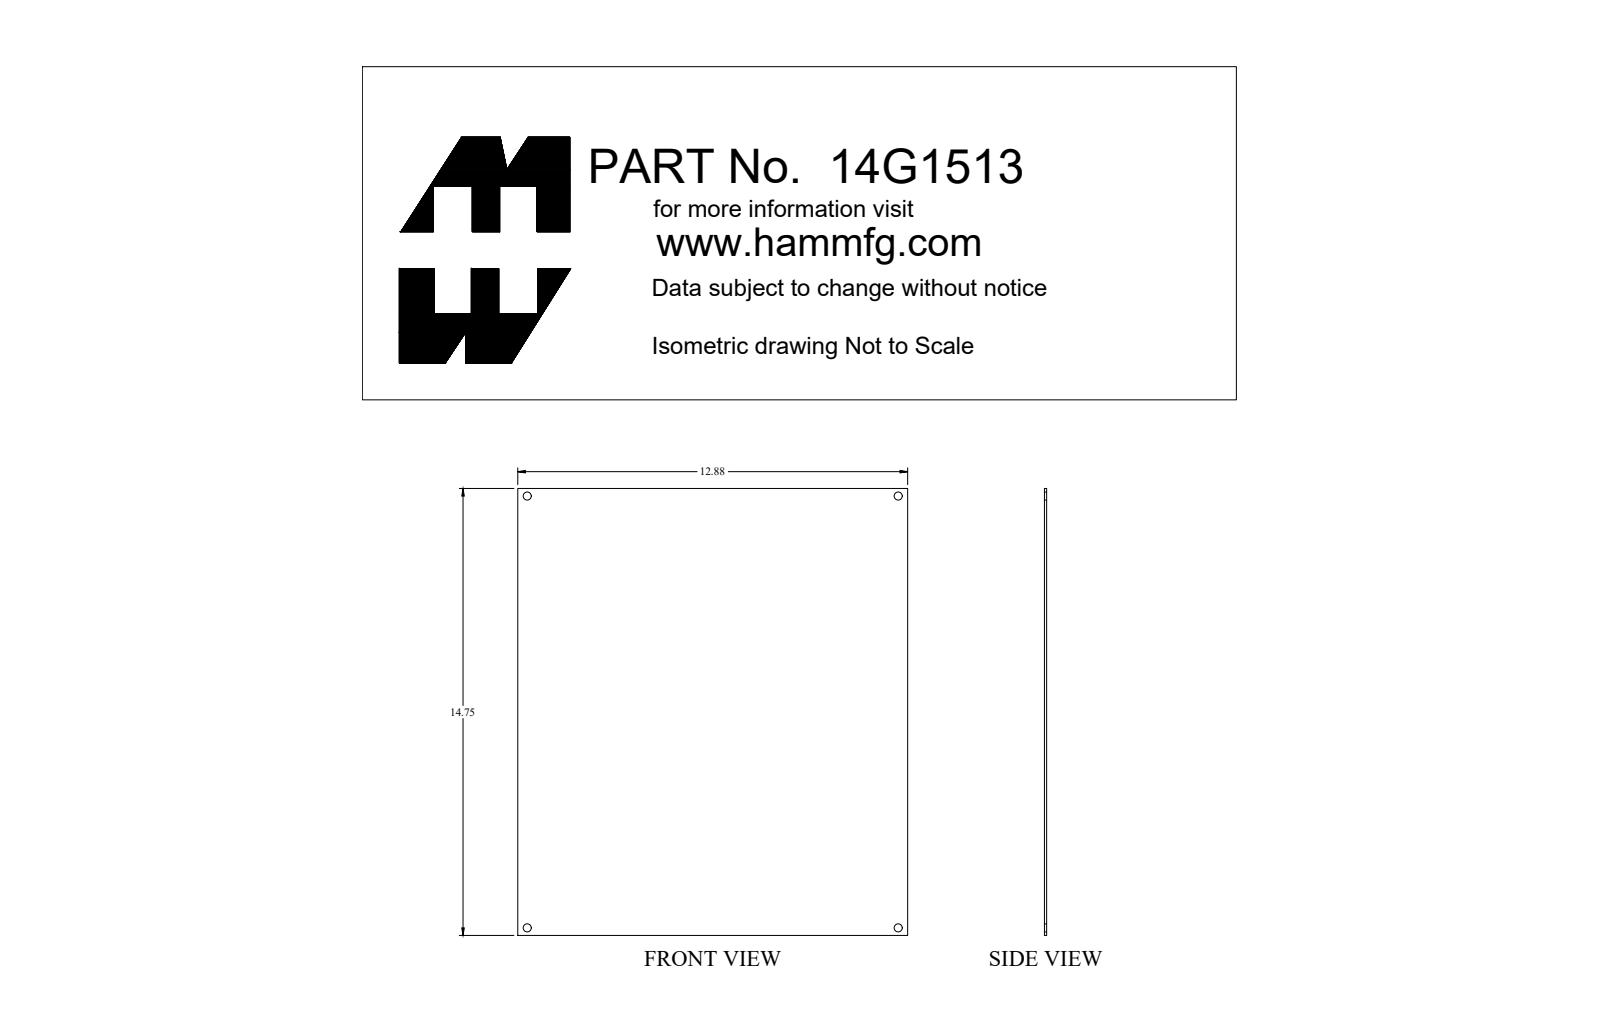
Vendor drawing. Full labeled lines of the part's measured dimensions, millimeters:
Part name (STEP PRODUCT): 14G1513
STEP written by: SolidWorks 2018 (AUTOMOTIVE_DESIGN)
Units: millimetres
Bodies: 1 solid, 10 faces (6 planar, 4 cylindrical, 0 other)
Overall size (bounding box): 374.7 × 327 × 1.8
Volume: 223 800 mm³ · Surface area: 247 500 mm²
Round holes (diameter × count): ⌀6.7 ×4
Main face-to-face distances: 1.8, 327, 374.7
Hole centre spacings: 311.2, 362, 477.3
